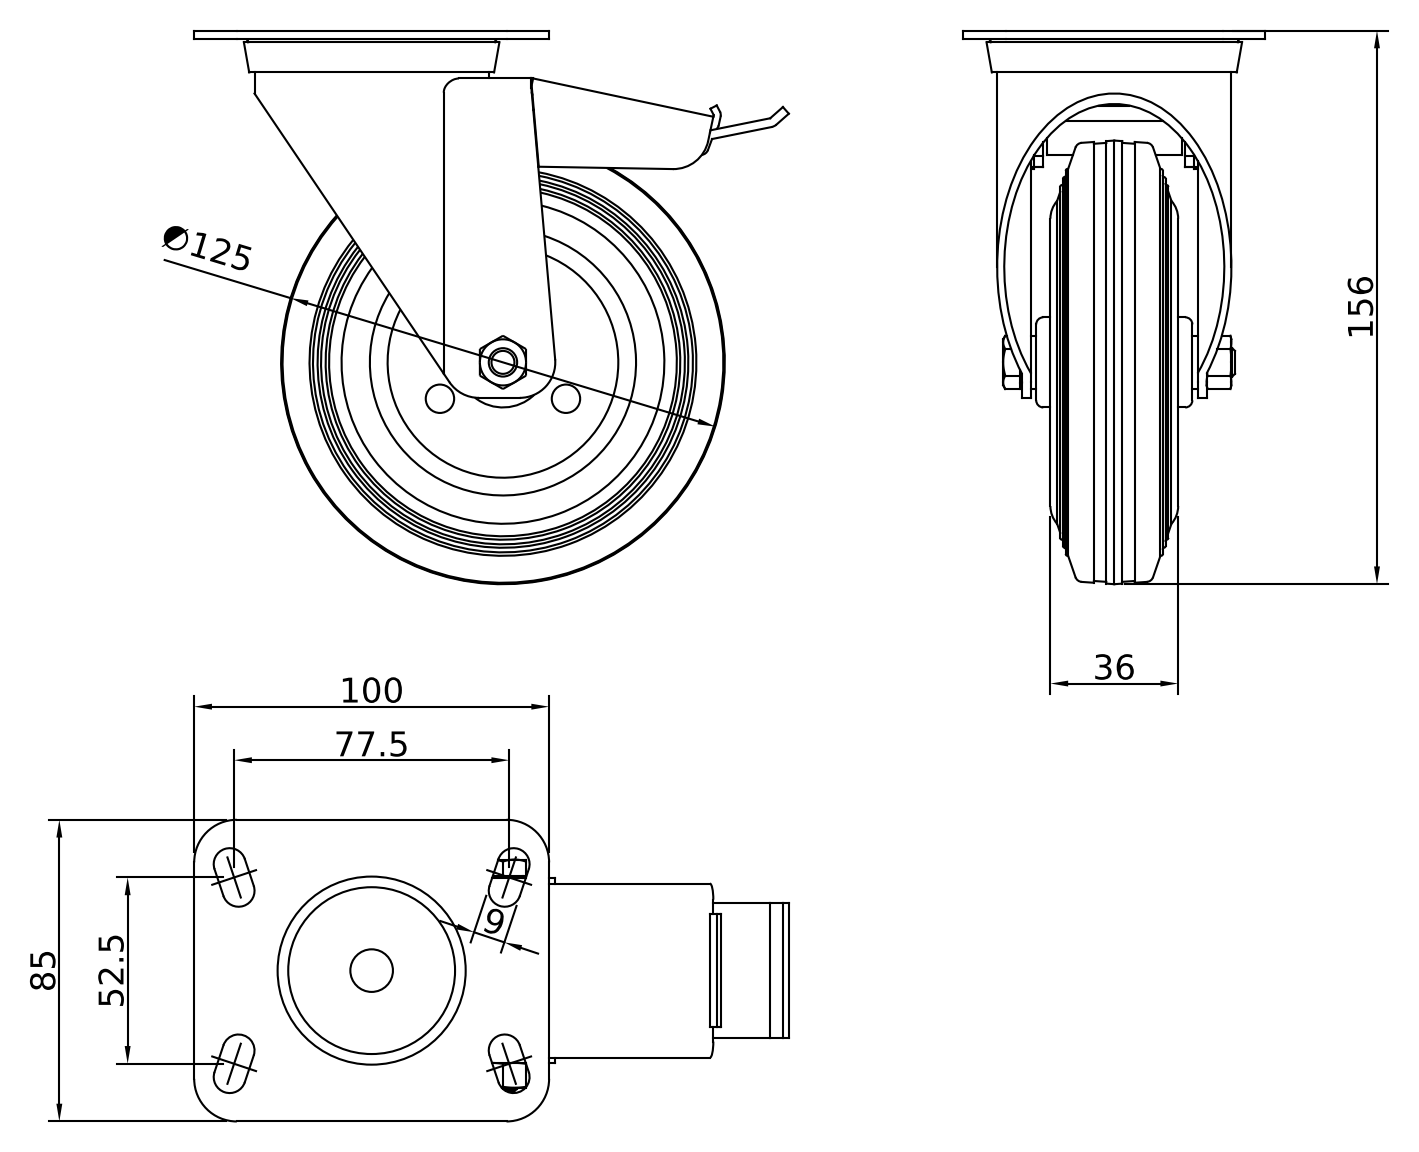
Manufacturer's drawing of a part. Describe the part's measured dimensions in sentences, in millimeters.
The part is named "CRUST0000040". Its 3-D file was written by "Autodesk Inventor 2022 (AUTOMOTIVE_DESIGN)". It is 6 solids with 288 faces: 153 planar, 60 cylindrical and 75 other. Overall it measures 167.54 by 156 by 85 millimeters. Its volume is 402 779 cubic millimeters and its surface area 109 448 square millimeters. Round holes: 1 of diameter 6.02, 1 of diameter 6.65, 1 of diameter 8, 1 of diameter 12, 1 of diameter 15, 1 of diameter 15.5, 1 of diameter 18, 1 of diameter 62, 1 of diameter 65. Round bosses or shafts: 1 of diameter 75, 1 of diameter 66, 1 of diameter 54, 1 of diameter 25.4, 1 of diameter 11.47, 1 of diameter 7.53. Partial cylindrical surfaces (rounded edges, fillets, slot ends): 10 of radius 4.5, 5 of radius 2, 4 of radius 12, 3 of radius 10, 2 of radius 1.5, 2 of radius 4, 1 of radius 0.38, 1 of radius 1.13. The main face-to-face distances are 2.5, 49.5, 1, 2, 47, 24.8, 16, 27.2, 22.3, 24.7. The hole center spacings are 21.
